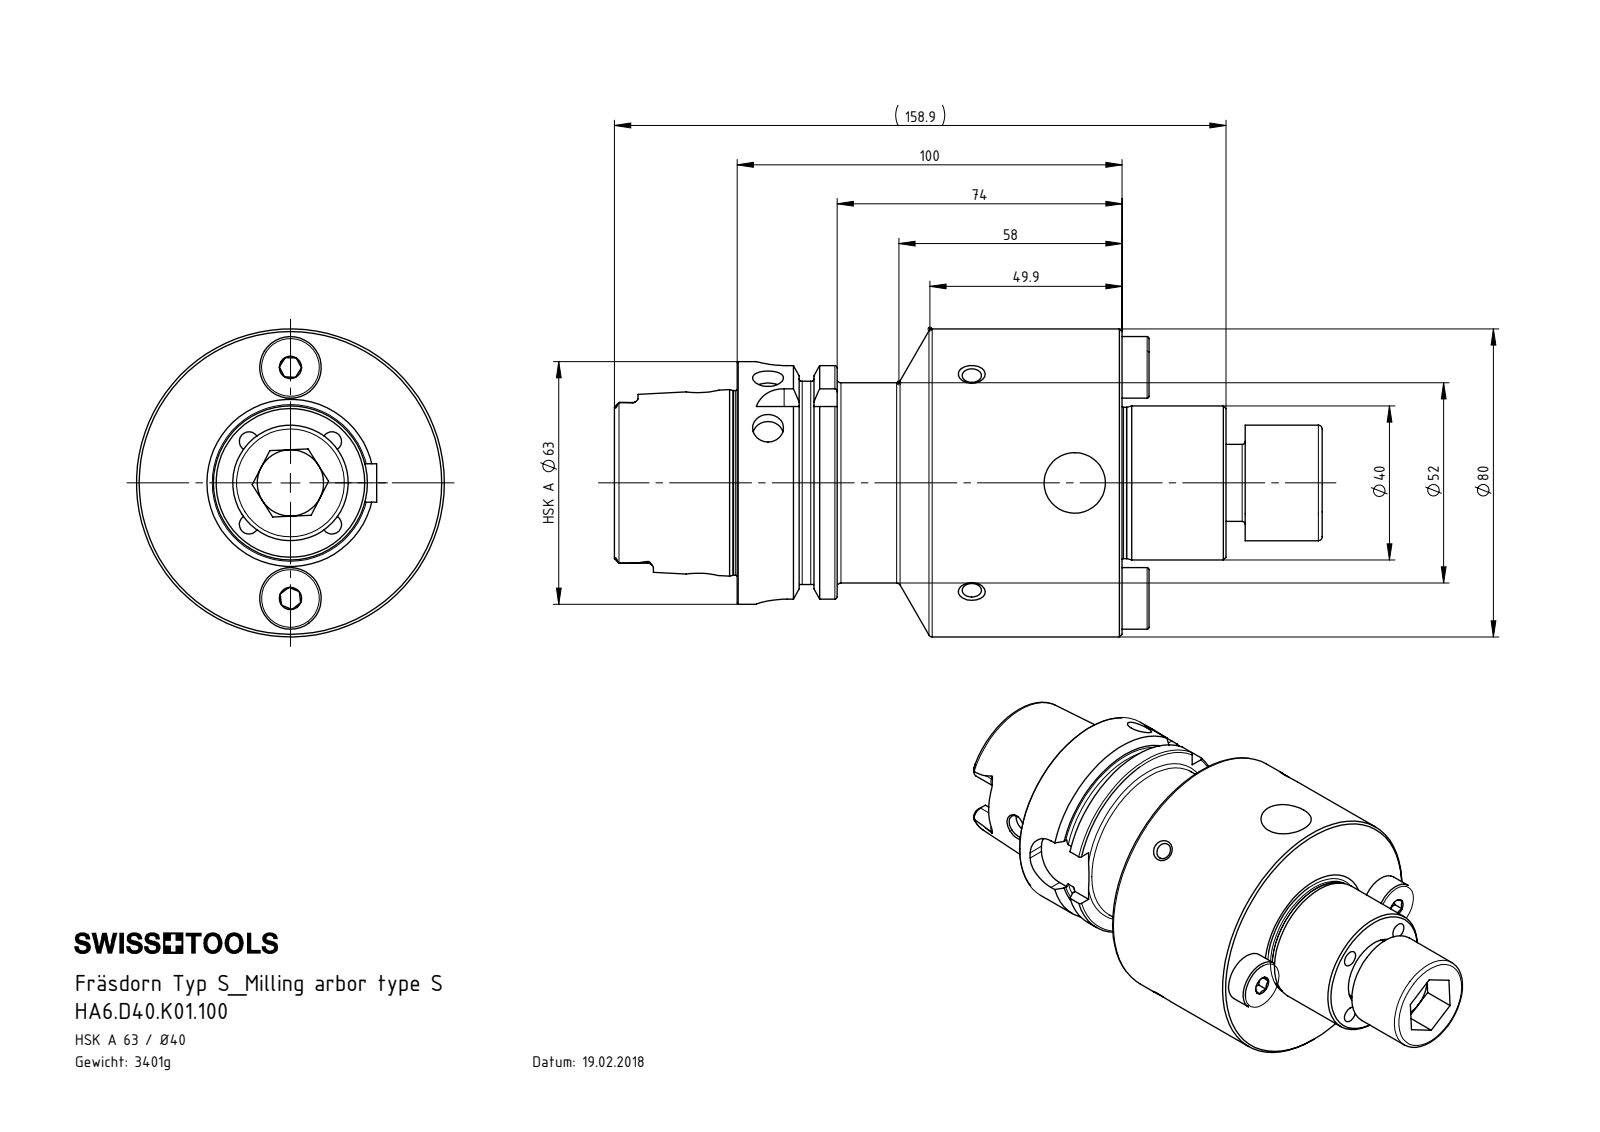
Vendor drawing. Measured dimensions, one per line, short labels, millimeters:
name: DIN 6885 - 10x8x20; D40-ER1.002.040_A; HA6-D40.K01.100_E_Fertigbearbeitung; D40-ER2.001.023_B (+1 more)
written by: SolidWorks 2017 (AUTOMOTIVE_DESIGN)
unit: mm
bodies: 5 solids, 393 faces (96 planar, 120 cylindrical, 177 other)
size: 183.9 × 80 × 80
volume: 433 245 mm³; area: 66 036 mm²
holes: 12× ⌀5, 2× ⌀8, 2× ⌀14, 1× ⌀7.5, 1× ⌀8.4, 1× ⌀10, 1× ⌀17, 1× ⌀17.5, 1× ⌀19, 1× ⌀21, 1× ⌀34, 1× ⌀40
bosses: 2× ⌀16, 2× ⌀6, 2× ⌀4.6, 1× ⌀80, 1× ⌀63, 1× ⌀54.95, 1× ⌀52, 1× ⌀47.94
rounds: 6× R1.4, 4× R2.88, 4× R5, 4× R8
face distances: 100, 127, 27, 25, 20, 74.05, 16, 25.95, 101.05, 7
hole spacings: 15.25, 21.56, 22.04, 28.05, 42.18, 30, 30.49, 60
